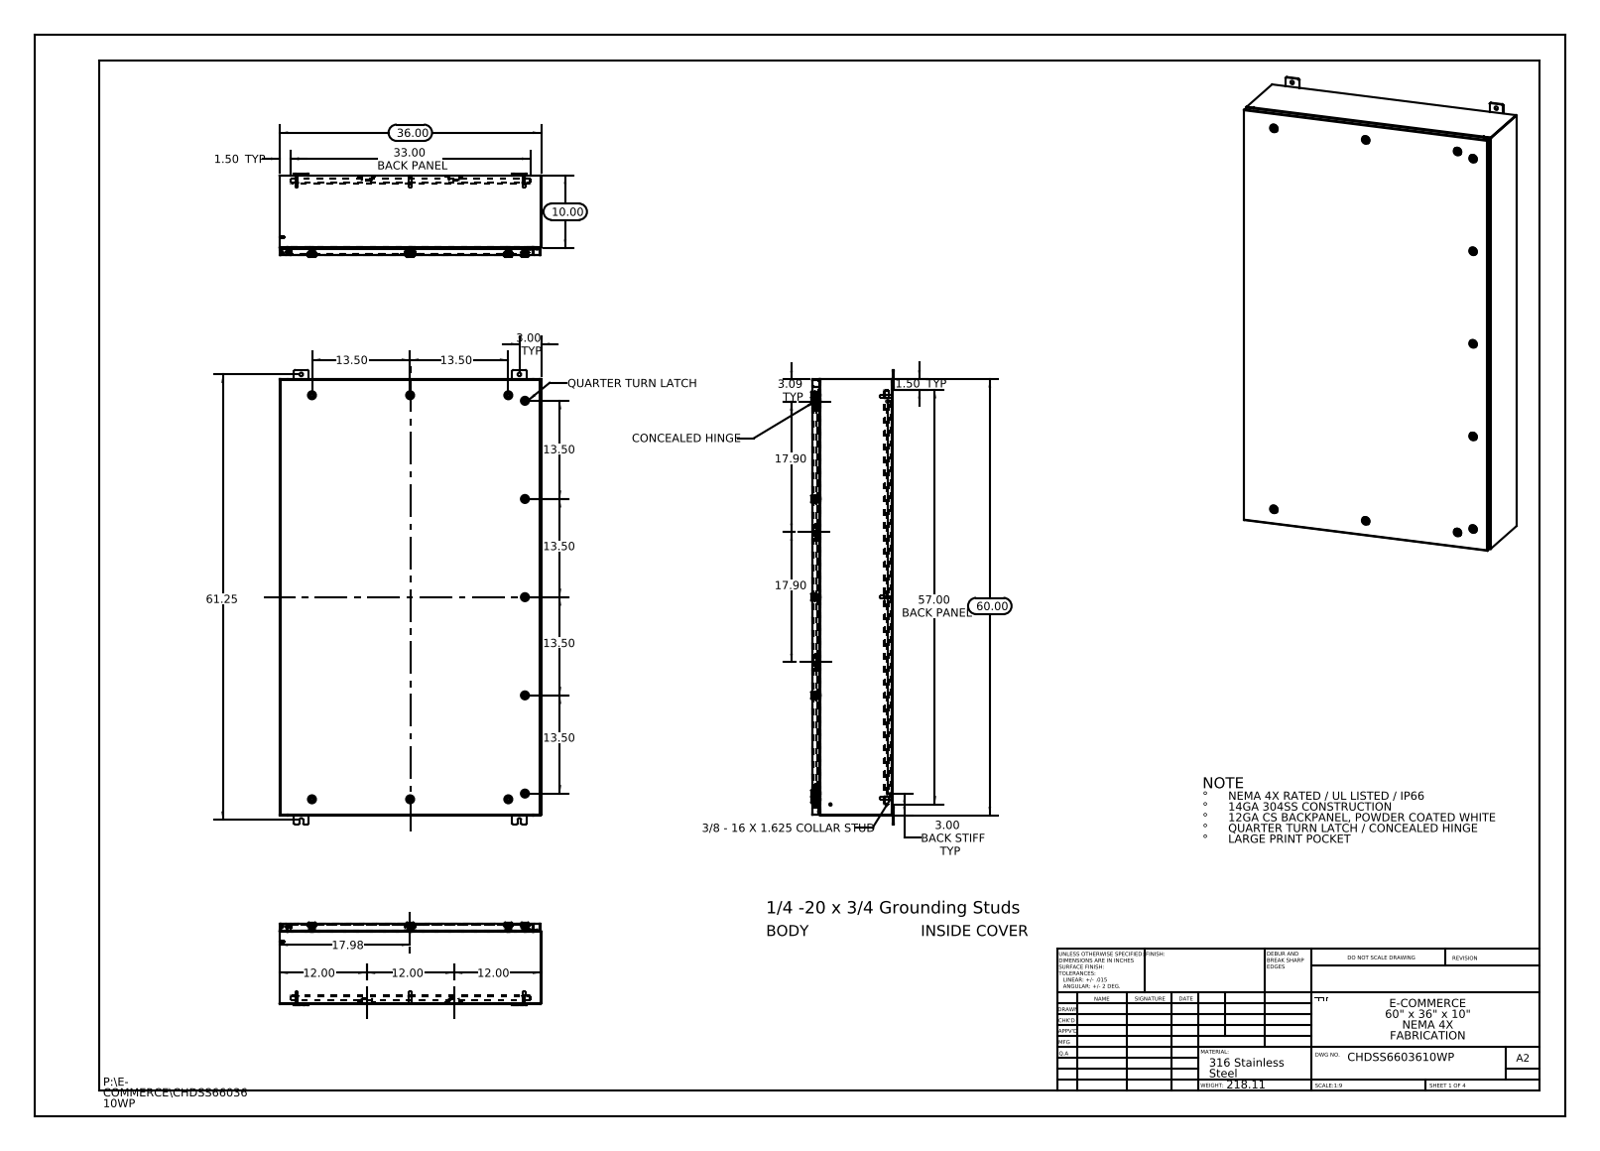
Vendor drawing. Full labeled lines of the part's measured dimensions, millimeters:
Part name (STEP PRODUCT): CHDSS6603610WP Backpanel; Washer-221320-IB-Industrilas_Washer-221320-IB-Industrilas; HW-CLH-E5-8004_Cam-232112-U-Industrilas; HW-CLH-R001-0500_2412-026240-2445-Industrilas (+8 more)
STEP written by: SolidWorks 2013 (CONFIG_CONTROL_DESIGN)
Units: millimetres
Bodies: 104 solids, 9960 faces (2880 planar, 3110 cylindrical, 3970 other)
Overall size (bounding box): 1587.5 × 914.4 × 288.4
Volume: 12 610 000 mm³ · Surface area: 12 280 000 mm²
Round holes (diameter × count): ⌀12.7 ×12, ⌀5 ×11, ⌀10 ×11, ⌀10.2 ×11, ⌀16 ×11, ⌀20 ×11, ⌀3.5 ×8, ⌀6.4 ×8, ⌀5.4 ×1
Round bosses / shafts (diameter × count): ⌀6 ×13, ⌀28 ×11, ⌀19.8 ×11, ⌀15.9 ×11, ⌀15.5 ×11, ⌀13.5 ×11, ⌀10 ×11, ⌀2.9 ×11
Partial cylindrical surfaces — rounded edges, fillets, slot ends (radius × count): R0.2 ×363, R3 ×363, R0.7 ×132, R0.5 ×44, R5 ×44, R0.3 ×34, R2.2 ×30, R4.8 ×24
Main face-to-face distances: 1.9, 1.9, 275.9, 277.8, 279.7, 277.7, 2.6, 25.4, 27.3, 250.5
Hole centre spacings: 342.9, 454.6, 17.5, 56.5, 685.8, 701.7, 909.1, 1059.4
